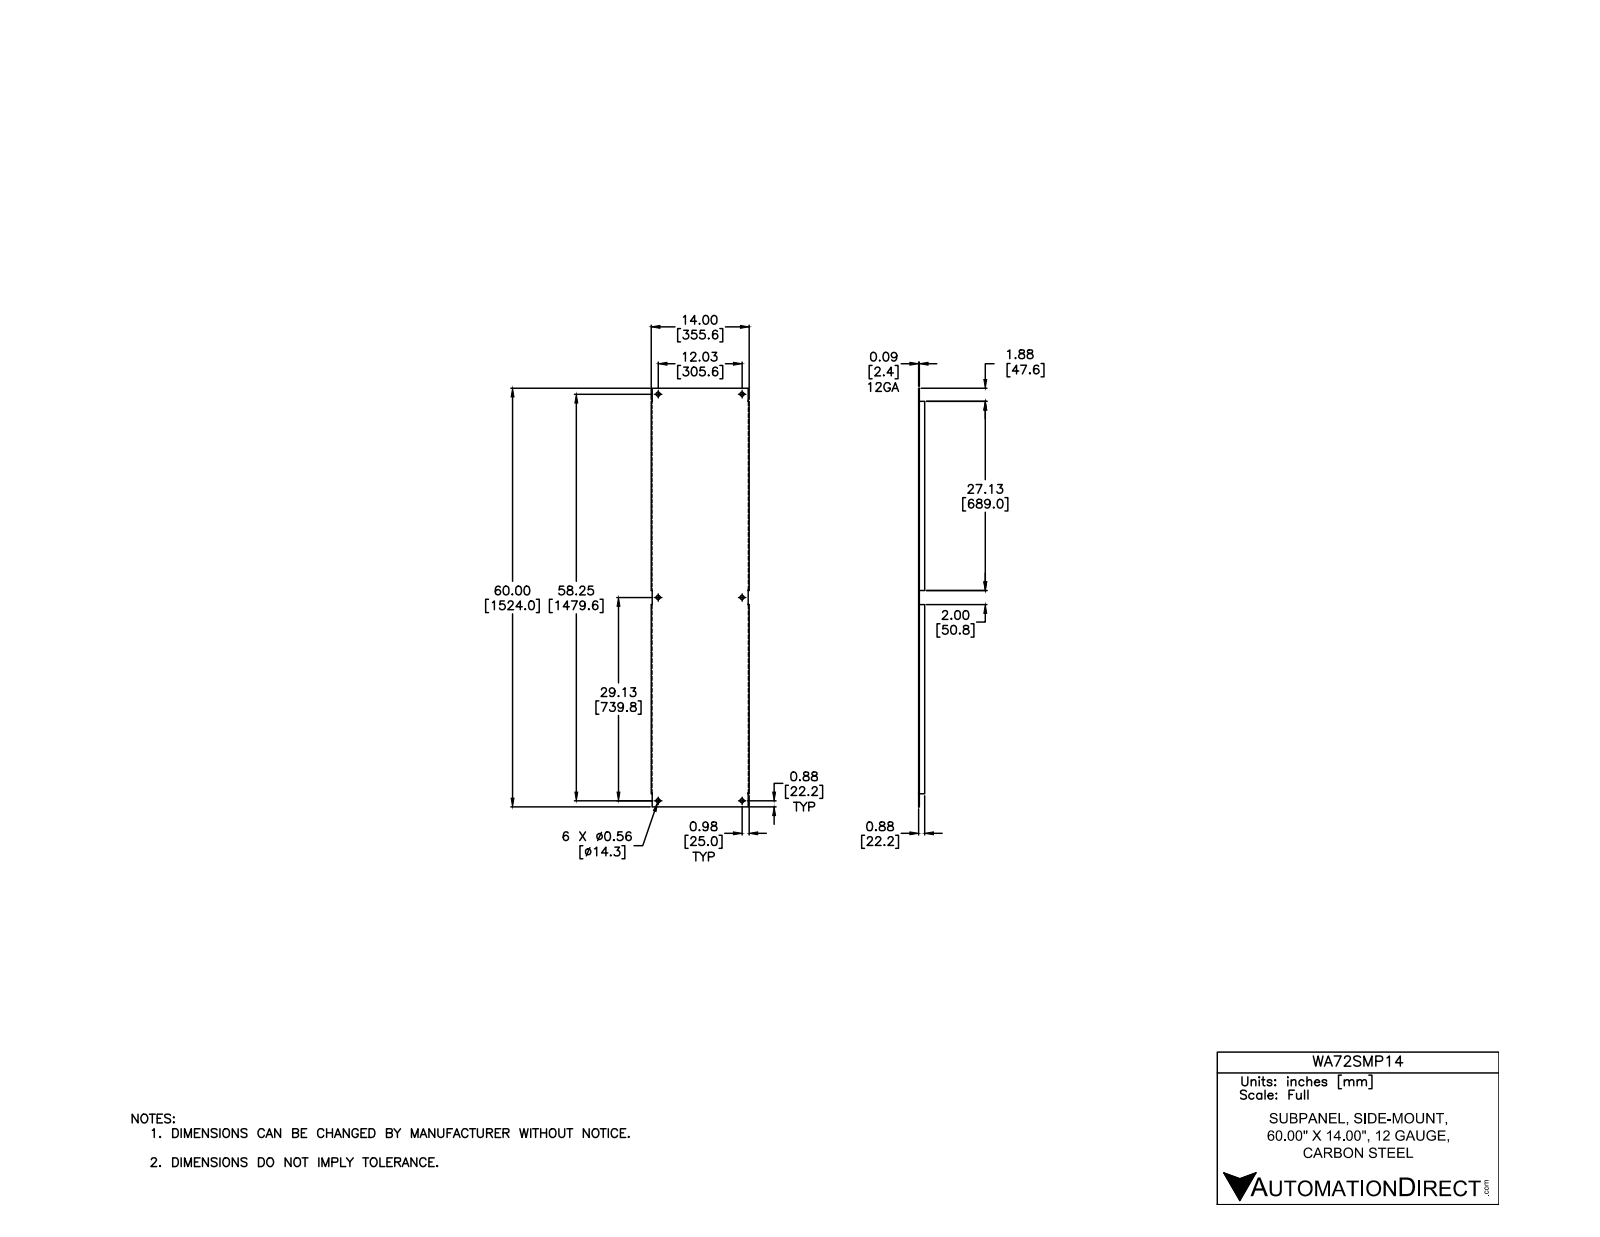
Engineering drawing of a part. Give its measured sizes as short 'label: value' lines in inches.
name: WA60SMP14-WA90SMP20
written by: Autodesk Inventor 2012 (AUTOMOTIVE_DESIGN)
unit: in
bodies: 1 solid, 48 faces (34 planar, 14 cylindrical, 0 other)
size: 60 × 14 × 0.875
volume: 86.17 in³; area: 1 854 in²
holes: 6× ⌀0.563
rounds: 2× R0.015, 2× R0.109
face distances: 0.094, 13.906, 13.813, 14, 0.781, 0.875, 60, 0.109, 13.891, 0.015
hole spacings: 29.125, 31.513, 12.032, 58.25, 59.48
